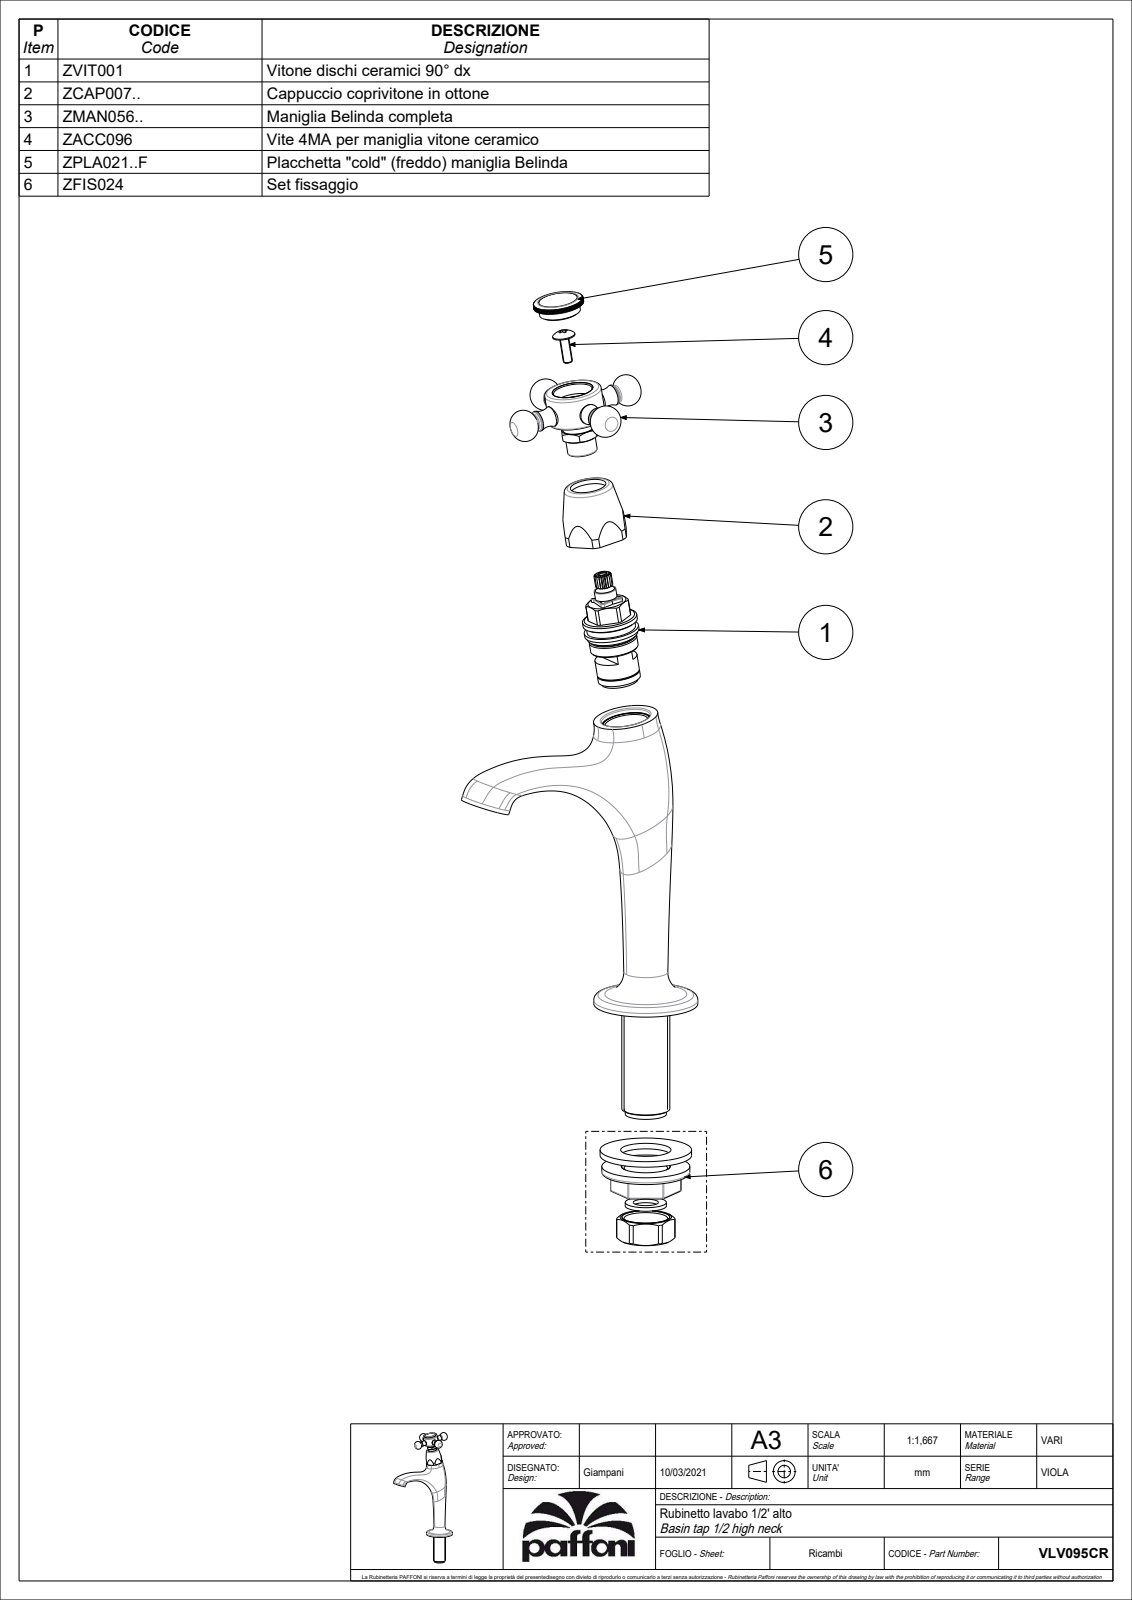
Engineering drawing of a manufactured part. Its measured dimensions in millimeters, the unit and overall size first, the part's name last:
Units: millimetres
Overall size (bounding box): 183.57 × 114.12 × 64.07
Round bosses / shafts (diameter × count): ⌀9 ×3, ⌀7 ×3, ⌀45.5 ×1, ⌀25 ×1, ⌀21.7 ×1, ⌀14 ×1, ⌀13 ×1
Partial cylindrical surfaces — rounded edges, fillets, slot ends (radius × count): R11 ×1, R14.5 ×1
Main face-to-face distances: 26.5, 11.2, 15, 20.74, 5.76, 5.74, 20.76, 5.75, 20.75, 15.2
Volume: 122 642 mm³ · Surface area: 24 854 mm²
Bodies: 1 solid, 483 faces (236 planar, 142 cylindrical, 105 other)
Part name (STEP PRODUCT): VLV095CR
STEP written by: CREO PARAMETRIC BY PTC INC, 2020044 (CONFIG_CONTROL_DESIGN)
